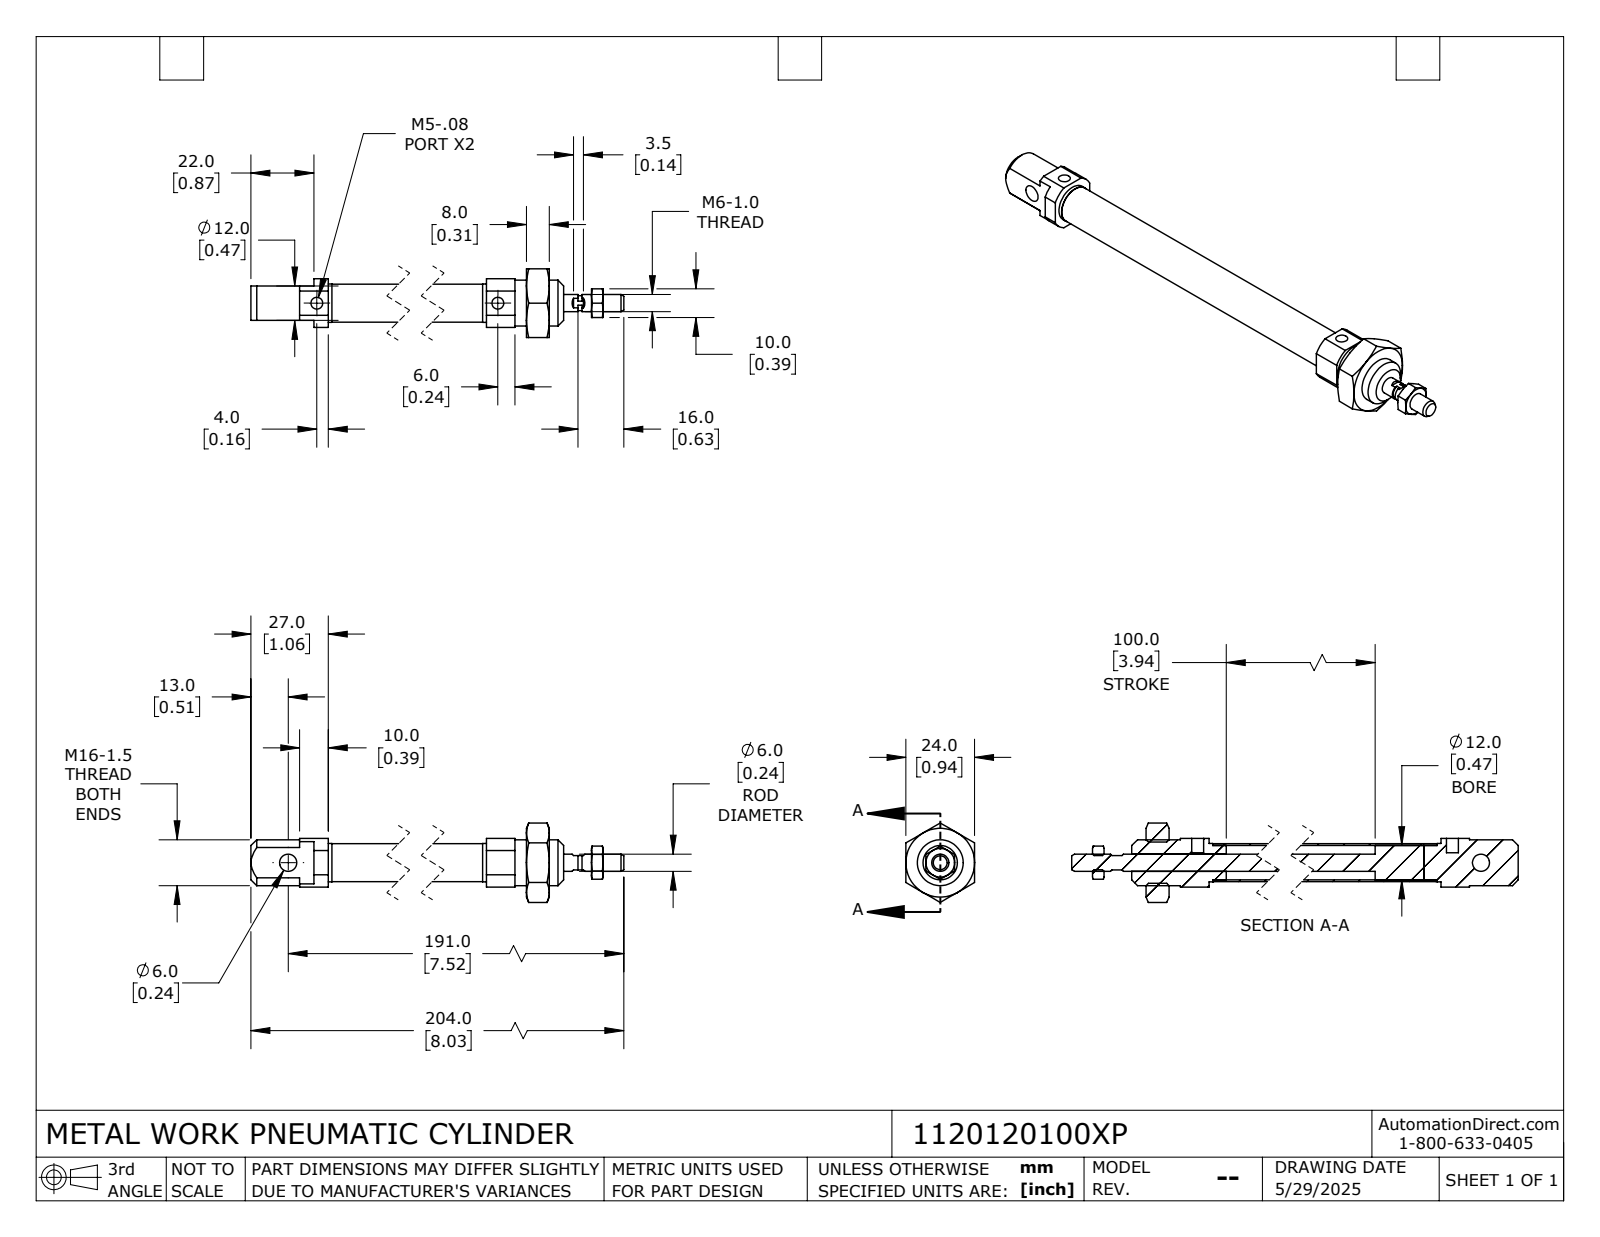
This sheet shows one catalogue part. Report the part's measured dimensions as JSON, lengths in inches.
{"part_name": "1120120100XP_ROD; 1120120100XP; 1120120100XP_BODY", "step_written_by": "SolidWorks 2024 (CONFIG_CONTROL_DESIGN)", "units": "inches", "bodies": {"solids": 6, "faces": 139, "planar": 56, "cylindrical": 45, "other": 38}, "overall_size": [8.031, 1.091, 0.945], "volume_in3": 1.432, "surface_area_in2": 32.37, "round_holes": [[0.163, 2], [0.194, 1], [0.236, 1], [0.566, 1]], "round_bosses_or_shafts": [[0.63, 1], [0.528, 1], [0.522, 1], [0.472, 1], [0.236, 1], [0.205, 1]], "partial_cylinders_radius": [[0.374, 1]], "face_to_face_distances": [0.669, 0.236, 0.945, 0.472, 6.142, 0.098, 0.571, 0.315, 0.138, 1.299], "hole_center_spacings": [5.394]}
